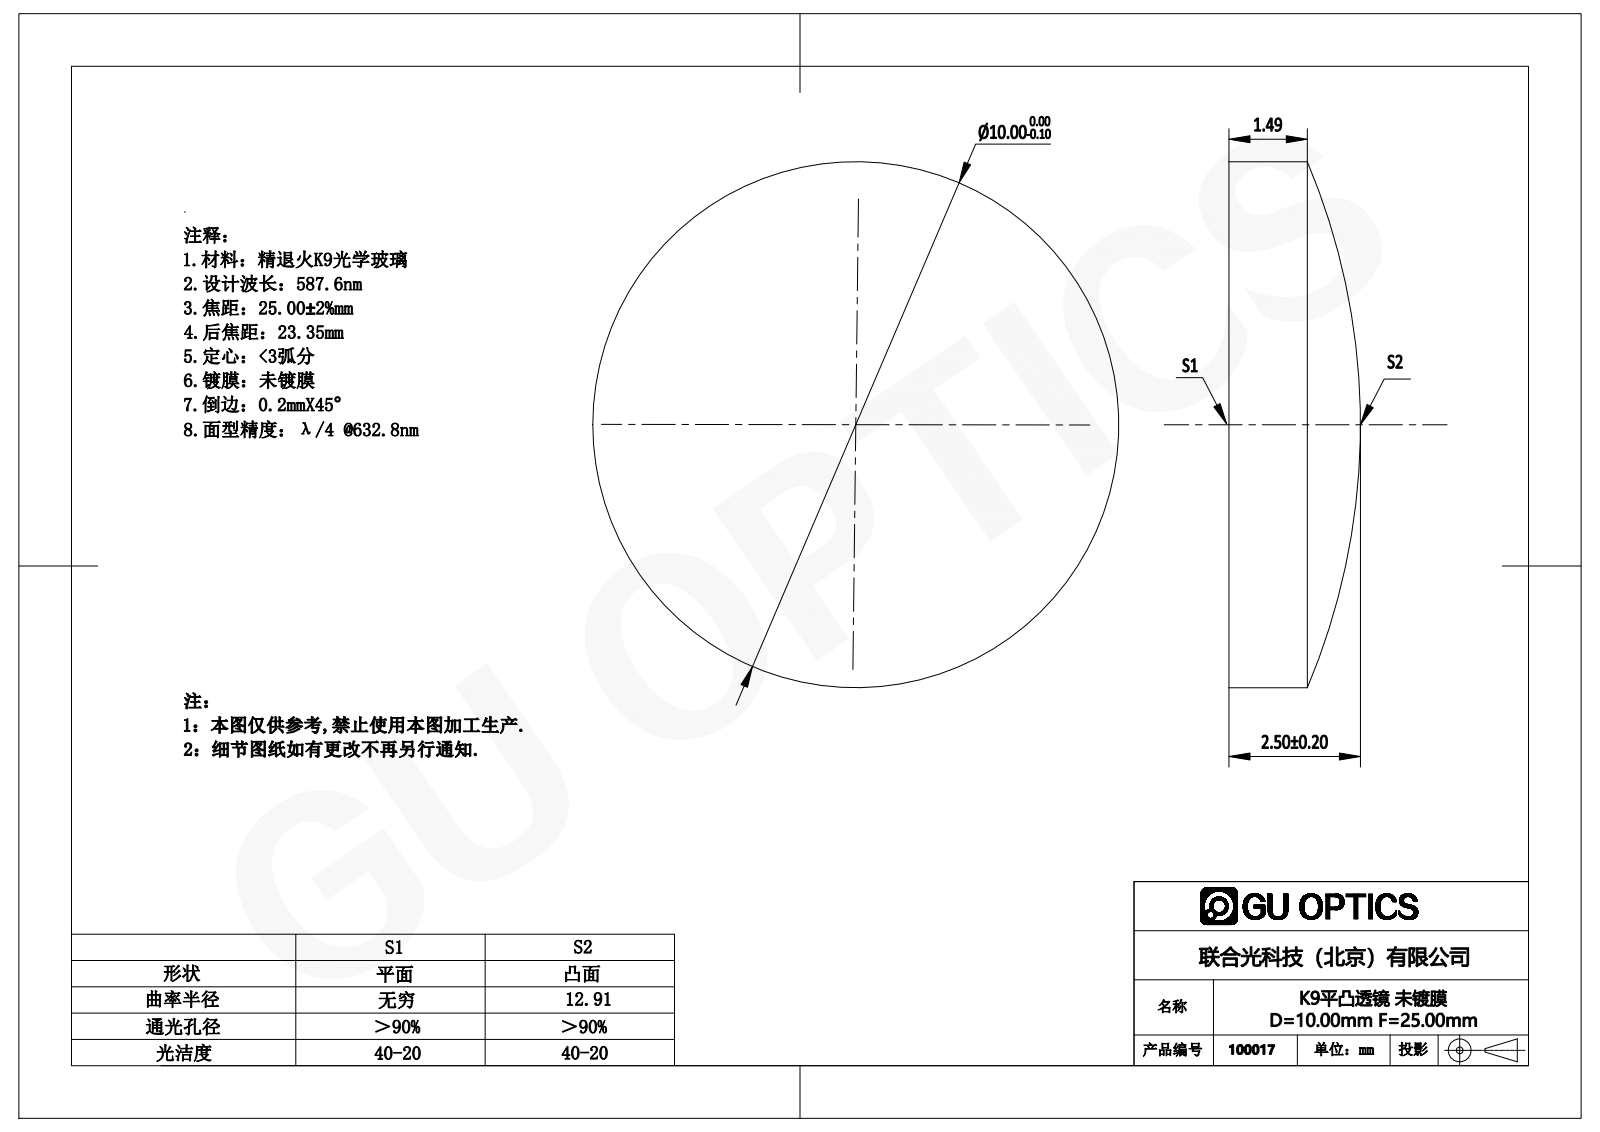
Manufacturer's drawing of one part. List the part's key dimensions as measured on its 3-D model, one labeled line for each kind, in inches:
Part name (STEP PRODUCT): 100017
STEP written by: SolidWorks 2016 (AUTOMOTIVE_DESIGN)
Units: inches
Bodies: 1 solid, 5 faces (1 planar, 2 cylindrical, 2 other)
Overall size (bounding box): 0.394 × 0.394 × 0.098
Volume: 0.01 in³ · Surface area: 0.321 in²
Round bosses / shafts (diameter × count): ⌀0.394 ×1
